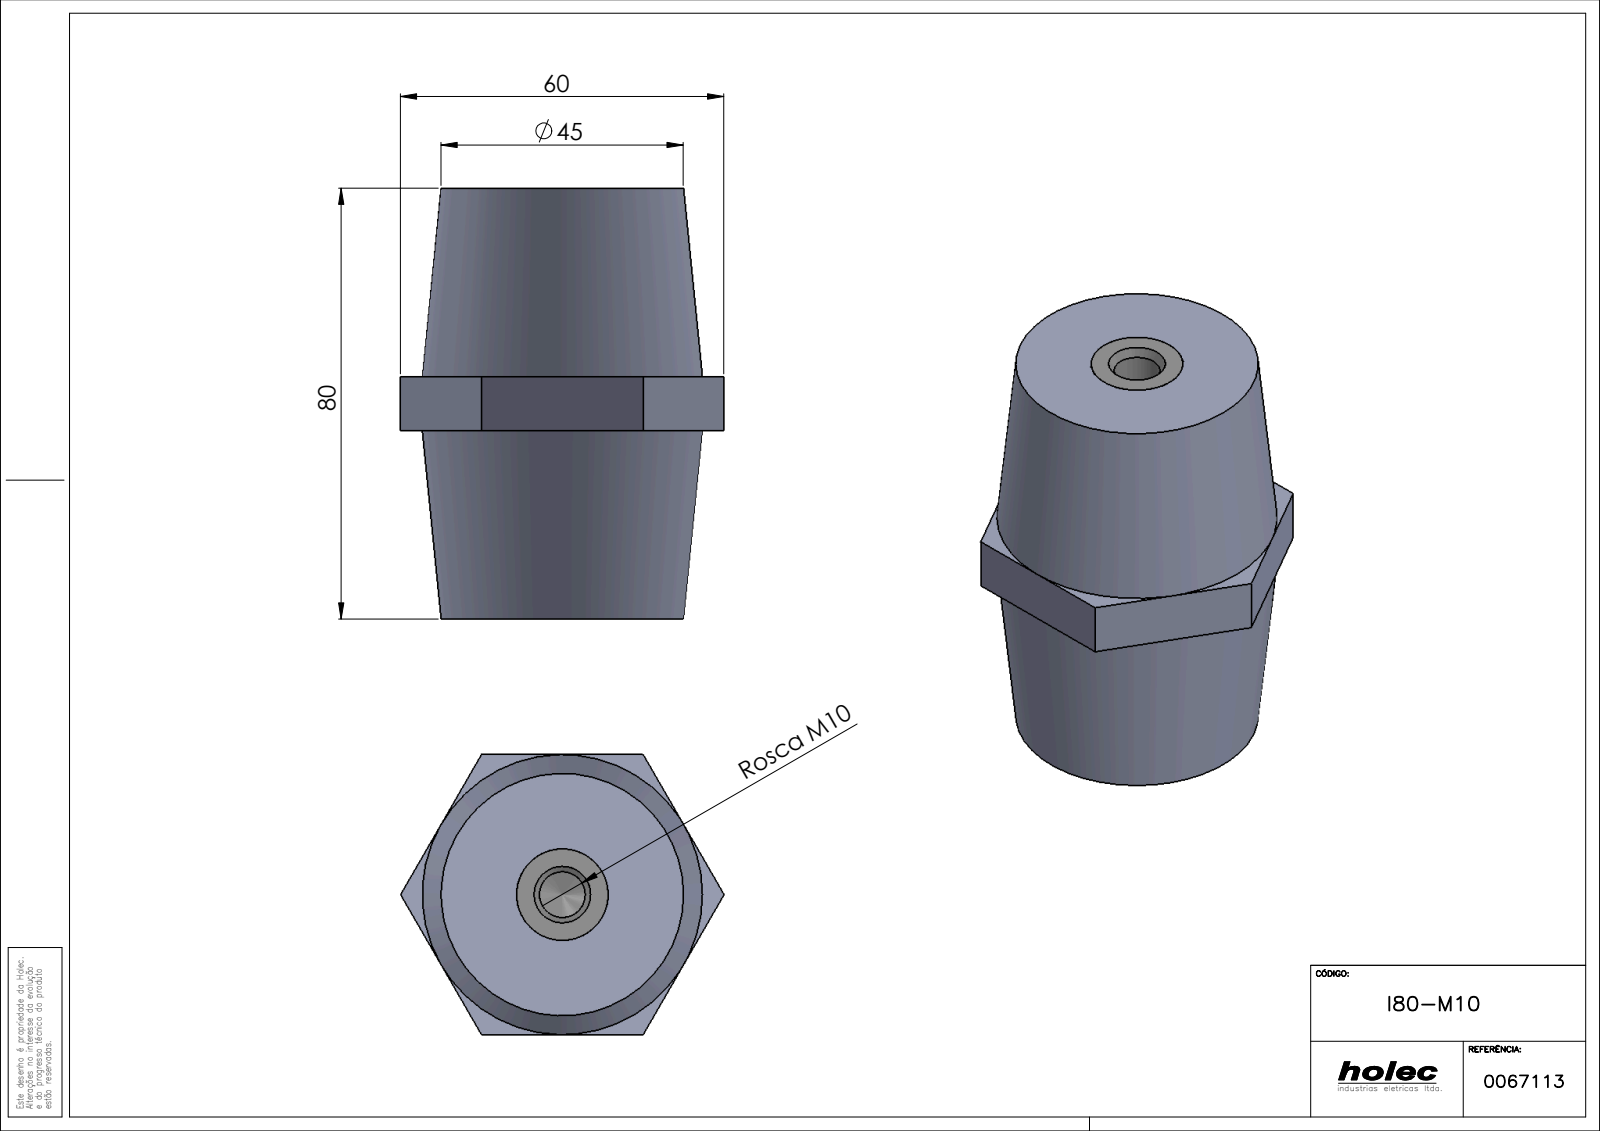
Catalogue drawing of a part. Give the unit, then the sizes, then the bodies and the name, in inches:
Units: inches
Overall size (bounding box): 3.15 × 2.364 × 2.047
Round holes (diameter × count): ⌀0.335 ×1, ⌀0.551 ×1
Main face-to-face distances: 0.669, 3.15, 2.047, 2.481, 2.48, 0.197, 0.472, 0.669, 1.811, 1.378
Volume: 9.229 in³ · Surface area: 34.38 in²
Bodies: 3 solids, 162 faces (82 planar, 12 cylindrical, 68 other)
Part name (STEP PRODUCT): I80-M10; PB1_0110(PB1_0111_10); PB1_0002
STEP written by: SolidWorks 2017 (AUTOMOTIVE_DESIGN)
